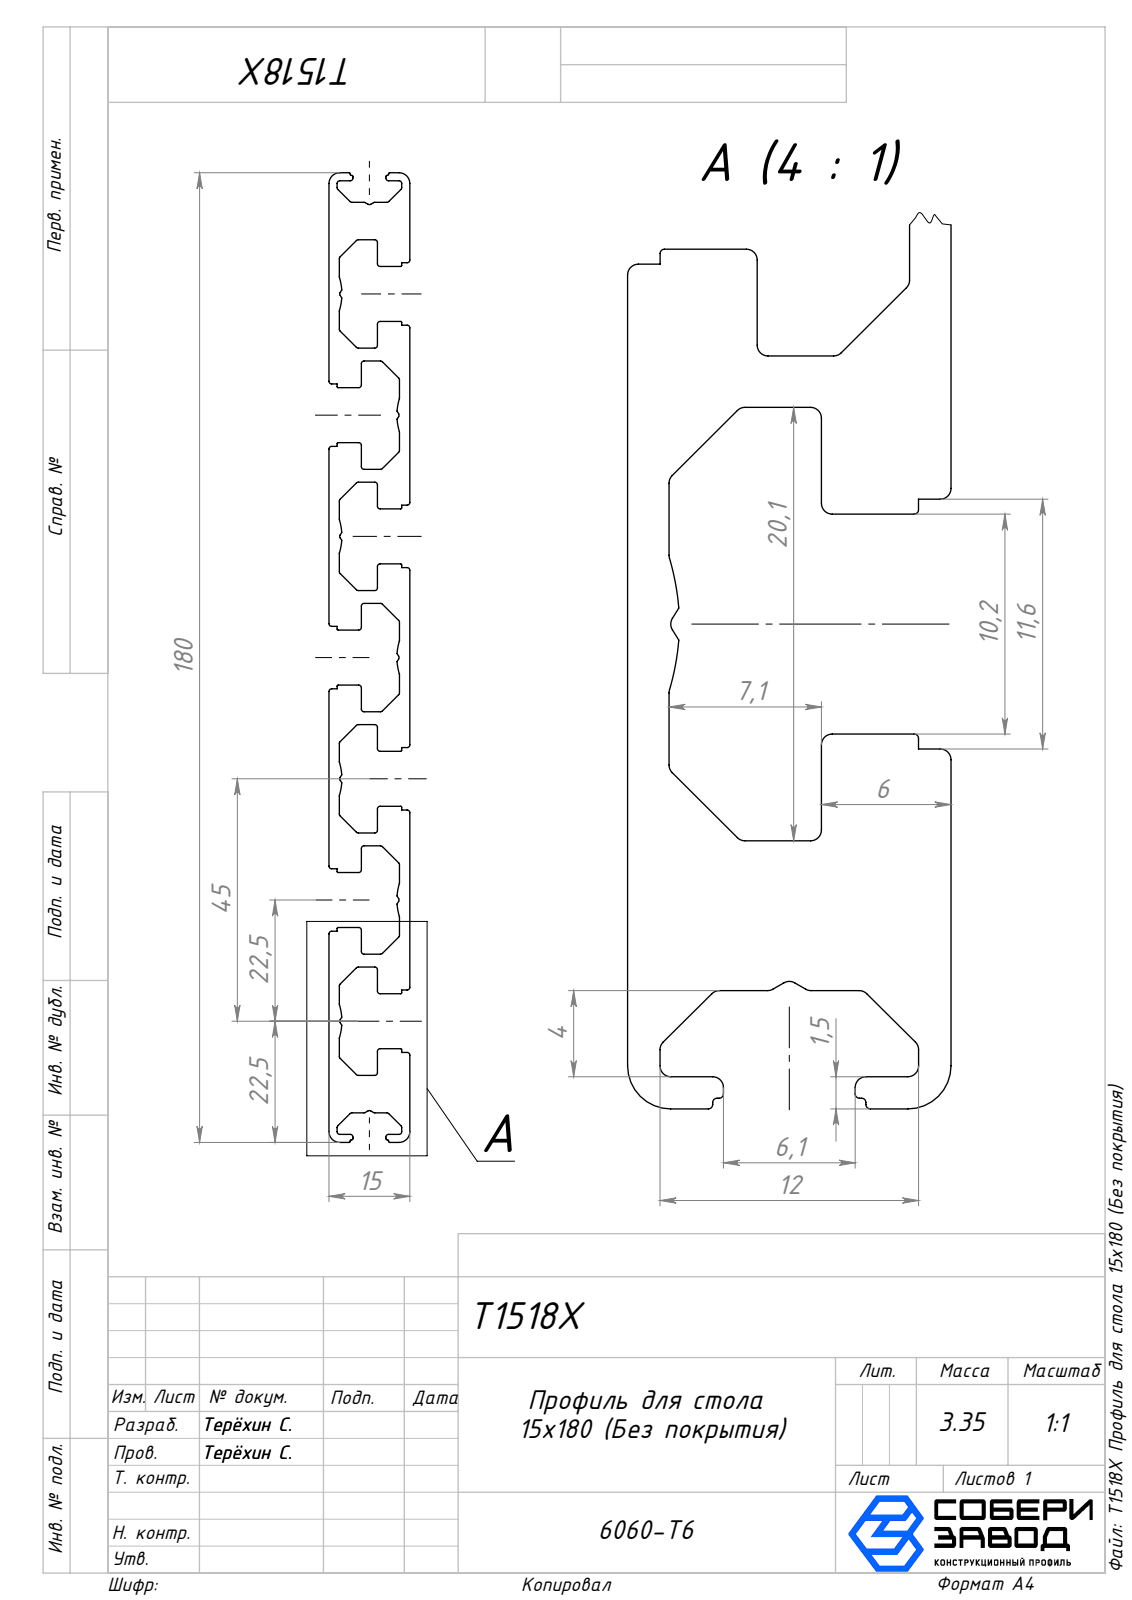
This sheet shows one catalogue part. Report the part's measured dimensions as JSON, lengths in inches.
{"part_name": "T1518X Профиль для стола 15х180 (Без покрытия)_00; T1518X Профиль для стола 15х180 (Без покрытия)", "step_written_by": "SolidWorks 2025 (CONFIG_CONTROL_DESIGN)", "units": "inches", "bodies": {"solids": 1, "faces": 317, "planar": 159, "cylindrical": 154, "other": 4}, "overall_size": [39.37, 7.087, 0.591], "volume_in3": 75.79, "surface_area_in2": 1103, "partial_cylinders_radius": [[0.02, 113], [0.008, 22], [0.453, 14], [0.079, 4]], "face_to_face_distances": [0.591, 0.237, 0.354, 0.076, 0.515, 0.278, 0.886, 0.161, 1.254, 1.772]}
